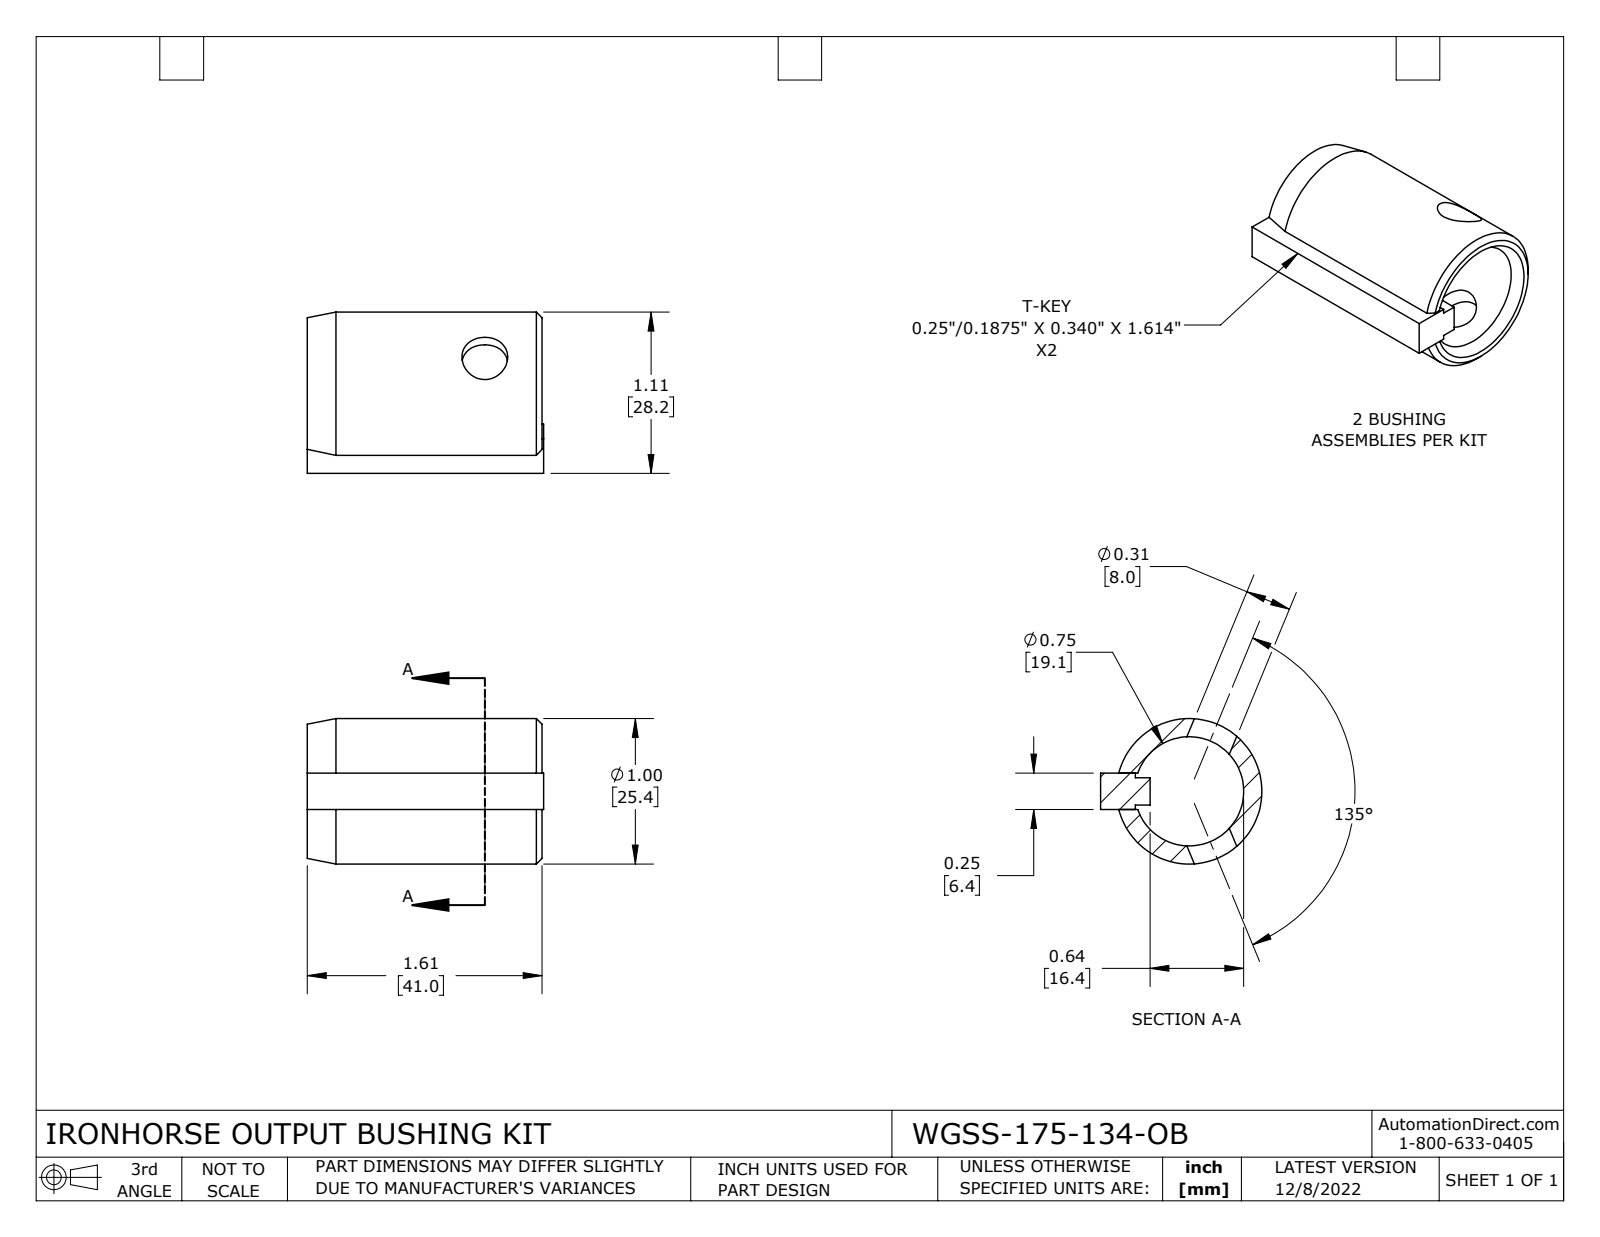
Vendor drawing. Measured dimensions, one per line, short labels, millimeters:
name: WGSS-175-134-OB
written by: SolidWorks 2021 (CONFIG_CONTROL_DESIGN)
unit: mm
bodies: 2 solids, 35 faces (14 planar, 10 cylindrical, 11 other)
size: 41.28 × 28.16 × 25.4
volume: 9 676 mm³; area: 6 954 mm²
holes: 2× ⌀8, 1× ⌀19.05
bosses: 1× ⌀25.4
face distances: 6.35, 8.63, 0.8, 5.55, 5.56, 4.76, 0.79, 2.58, 6.05, 41
